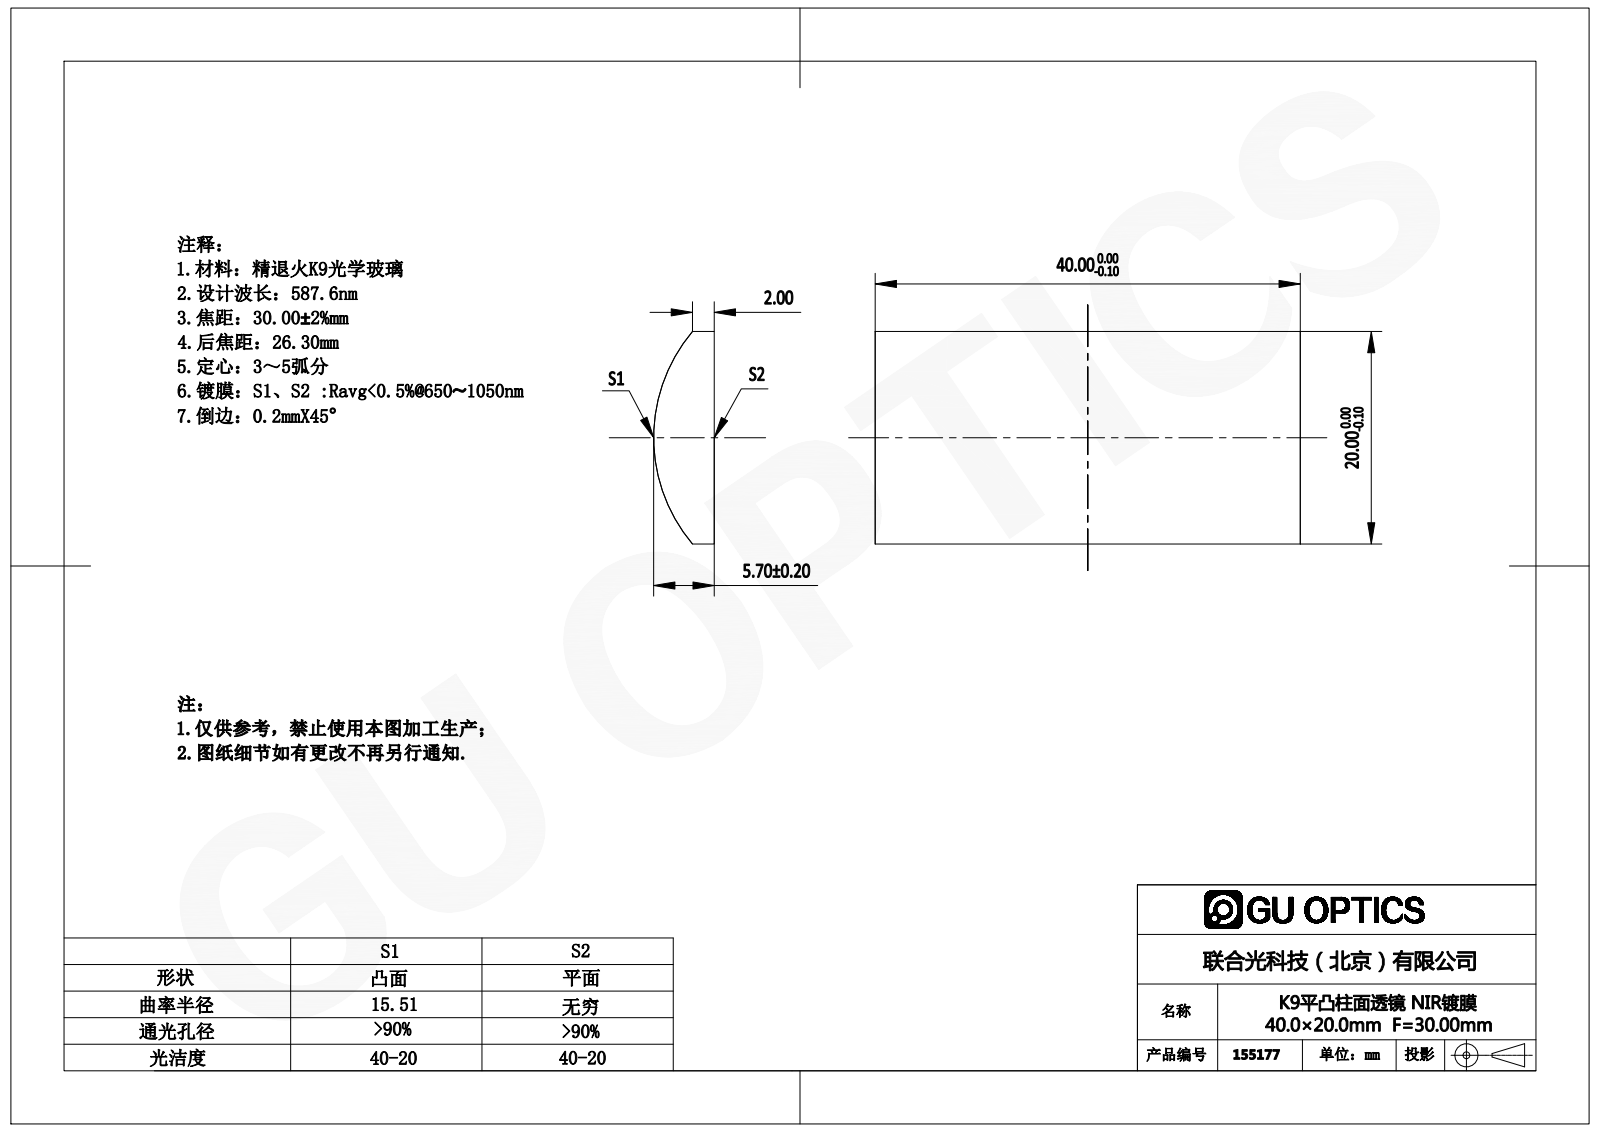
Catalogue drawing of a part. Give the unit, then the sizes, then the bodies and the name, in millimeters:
Units: millimetres
Overall size (bounding box): 40 × 20 × 5.7
Partial cylindrical surfaces — rounded edges, fillets, slot ends (radius × count): R15.51 ×1
Main face-to-face distances: 40, 20
Volume: 3 637 mm³ · Surface area: 2 015 mm²
Bodies: 1 solid, 6 faces (5 planar, 1 cylindrical, 0 other)
Part name (STEP PRODUCT): 155045
STEP written by: SolidWorks 2016 (AUTOMOTIVE_DESIGN)
